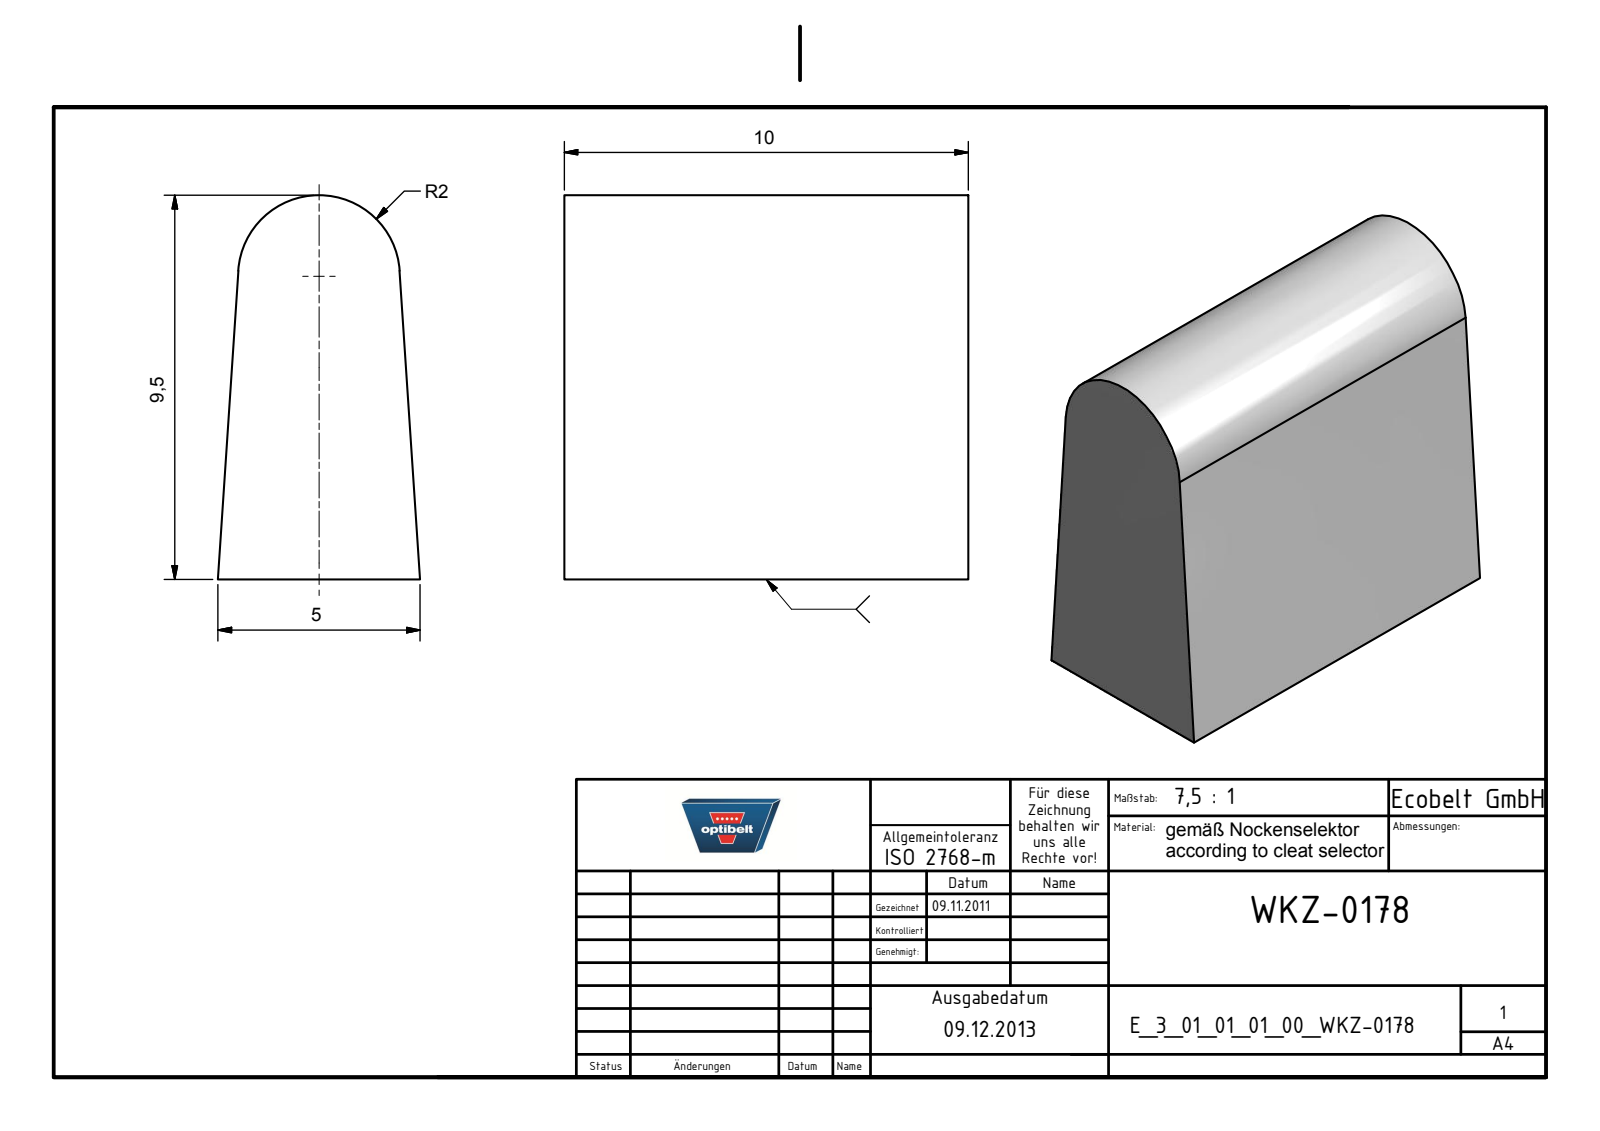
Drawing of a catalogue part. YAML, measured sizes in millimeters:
part_name: "E_3_01_01_01_00_WKZ-0178"
step_written_by: "Autodesk Inventor 2021 (AUTOMOTIVE_DESIGN)"
units: millimeters
bodies: {solids: 1, faces: 6, planar: 5, cylindrical: 1, other: 0}
overall_size: [10, 9.5, 5]
volume: 401
surface_area: 343
partial_cylinders:
  - {radius: 2, count: 1}
face_to_face_distances: [10]
